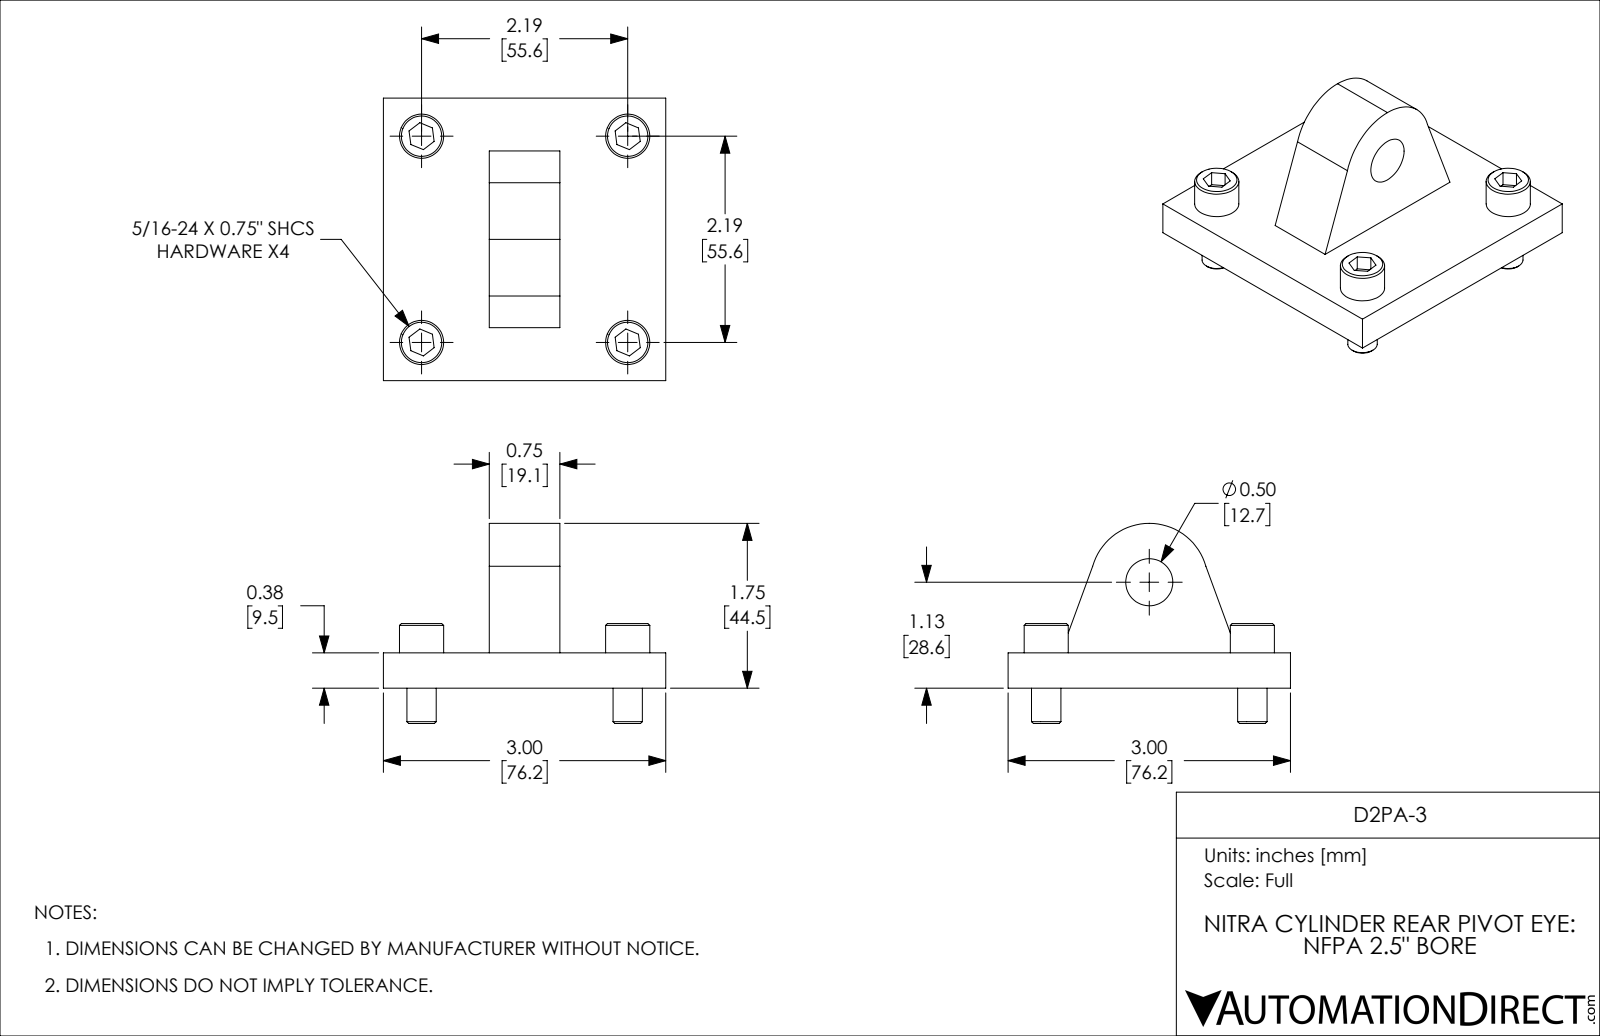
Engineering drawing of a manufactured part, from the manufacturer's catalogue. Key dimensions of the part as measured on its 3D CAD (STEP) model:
Part name (STEP PRODUCT): D2PA-3
STEP written by: SolidWorks 2019 (CONFIG_CONTROL_DESIGN)
Units: inches
Bodies: 5 solids, 94 faces (50 planar, 28 cylindrical, 16 other)
Overall size (bounding box): 3 × 3 × 2.125
Volume: 4.863 in³ · Surface area: 35.66 in²
Round holes (diameter × count): ⌀0.344 ×4, ⌀0.5 ×1
Round bosses / shafts (diameter × count): ⌀0.469 ×4, ⌀0.312 ×4
Partial cylindrical surfaces — rounded edges, fillets, slot ends (radius × count): R0.625 ×1
Main face-to-face distances: 0.375, 1.125, 1.875, 3, 0.75, 0.156, 0.312, 0.687, 0.25, 1.062
Hole centre spacings: 2.19, 3.097
